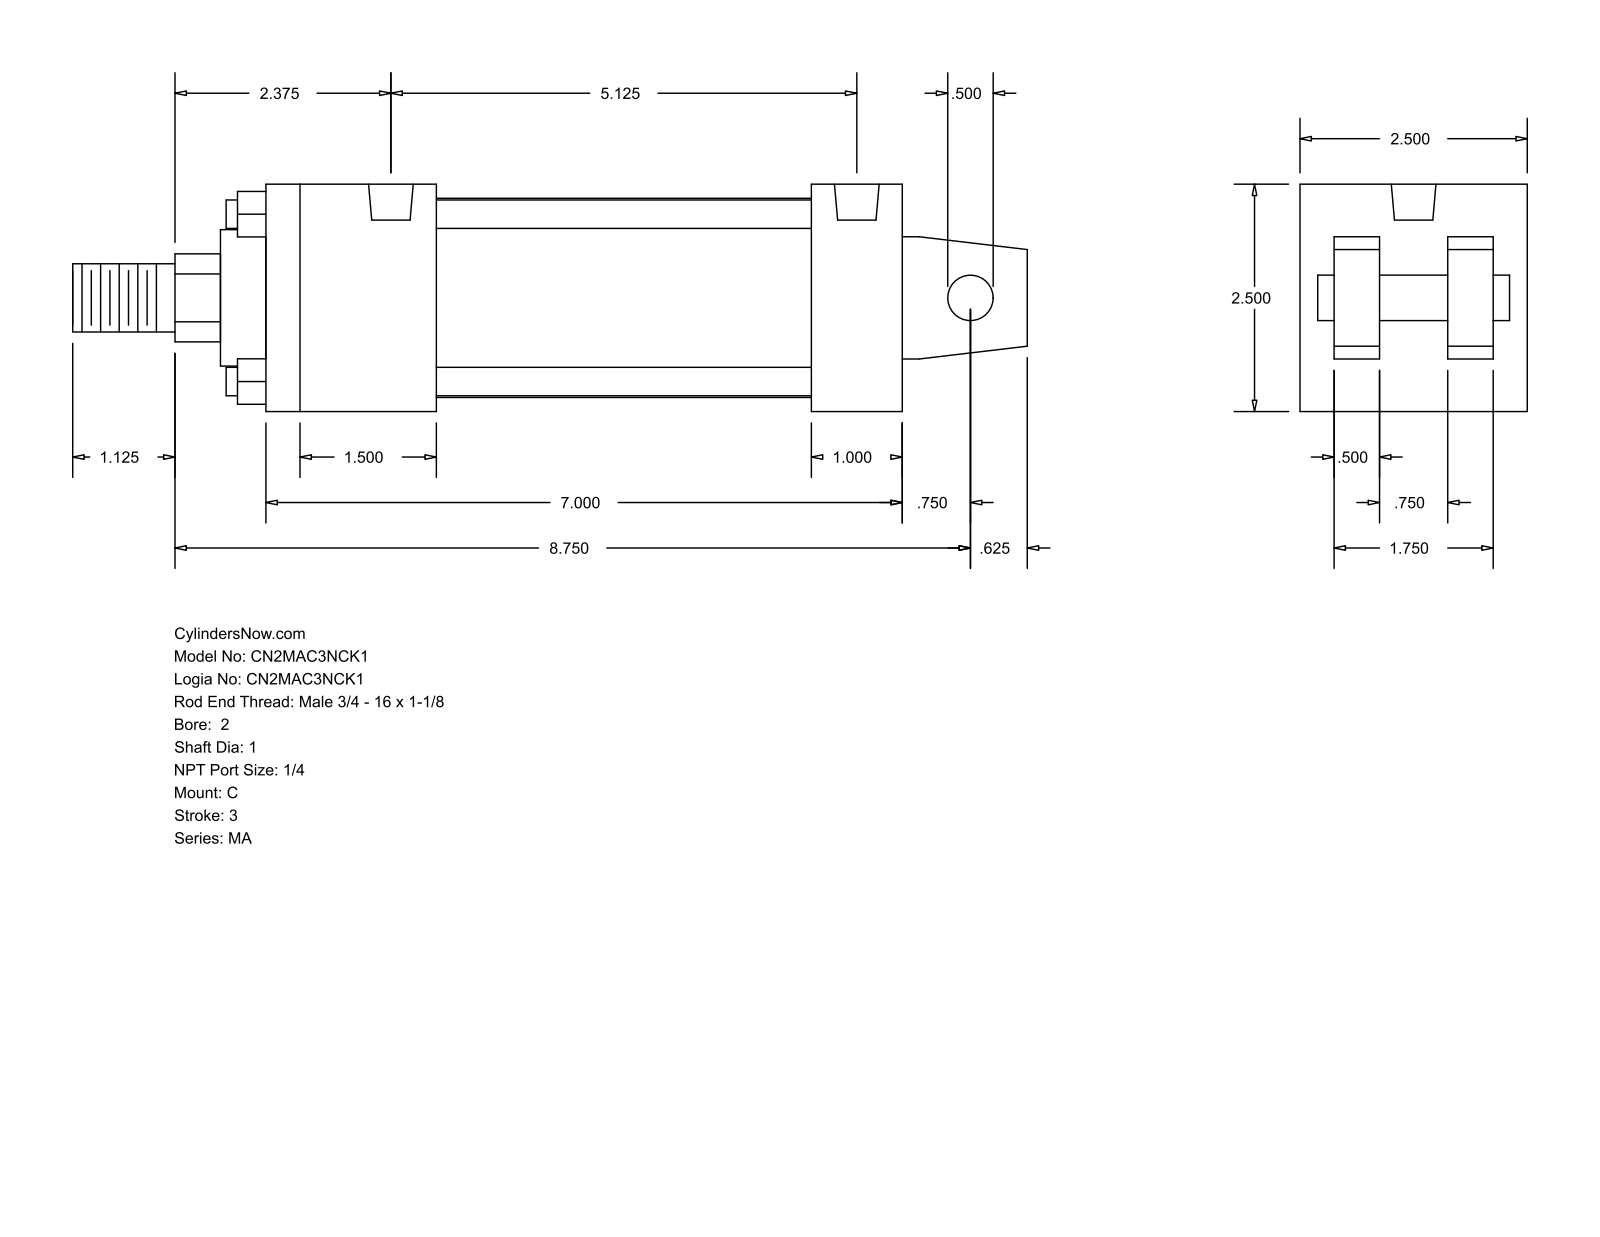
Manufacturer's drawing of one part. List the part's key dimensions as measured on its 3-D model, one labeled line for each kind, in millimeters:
Part name (STEP PRODUCT): MA_C__0200_1
STEP written by: GSSL Pune (CONFIG_CONTROL_DESIGN)
Units: millimetres
Bodies: 0 solids, 103 faces (76 planar, 27 cylindrical, 0 other)
Overall size (bounding box): 266.7 × 63.5 × 63.5
Round holes (diameter × count): ⌀7.94 ×4, ⌀12.49 ×2
Round bosses / shafts (diameter × count): ⌀7.94 ×4, ⌀55.63 ×1, ⌀38.1 ×1, ⌀25.4 ×1, ⌀19.05 ×1, ⌀12.7 ×1
Partial cylindrical surfaces — rounded edges, fillets, slot ends (radius × count): R12.29 ×1
Main face-to-face distances: 63.5, 12.7, 177.8, 22.22, 41.28, 9.52, 53.98, 31.76, 47.63, 25.4
Hole centre spacings: 130.17
